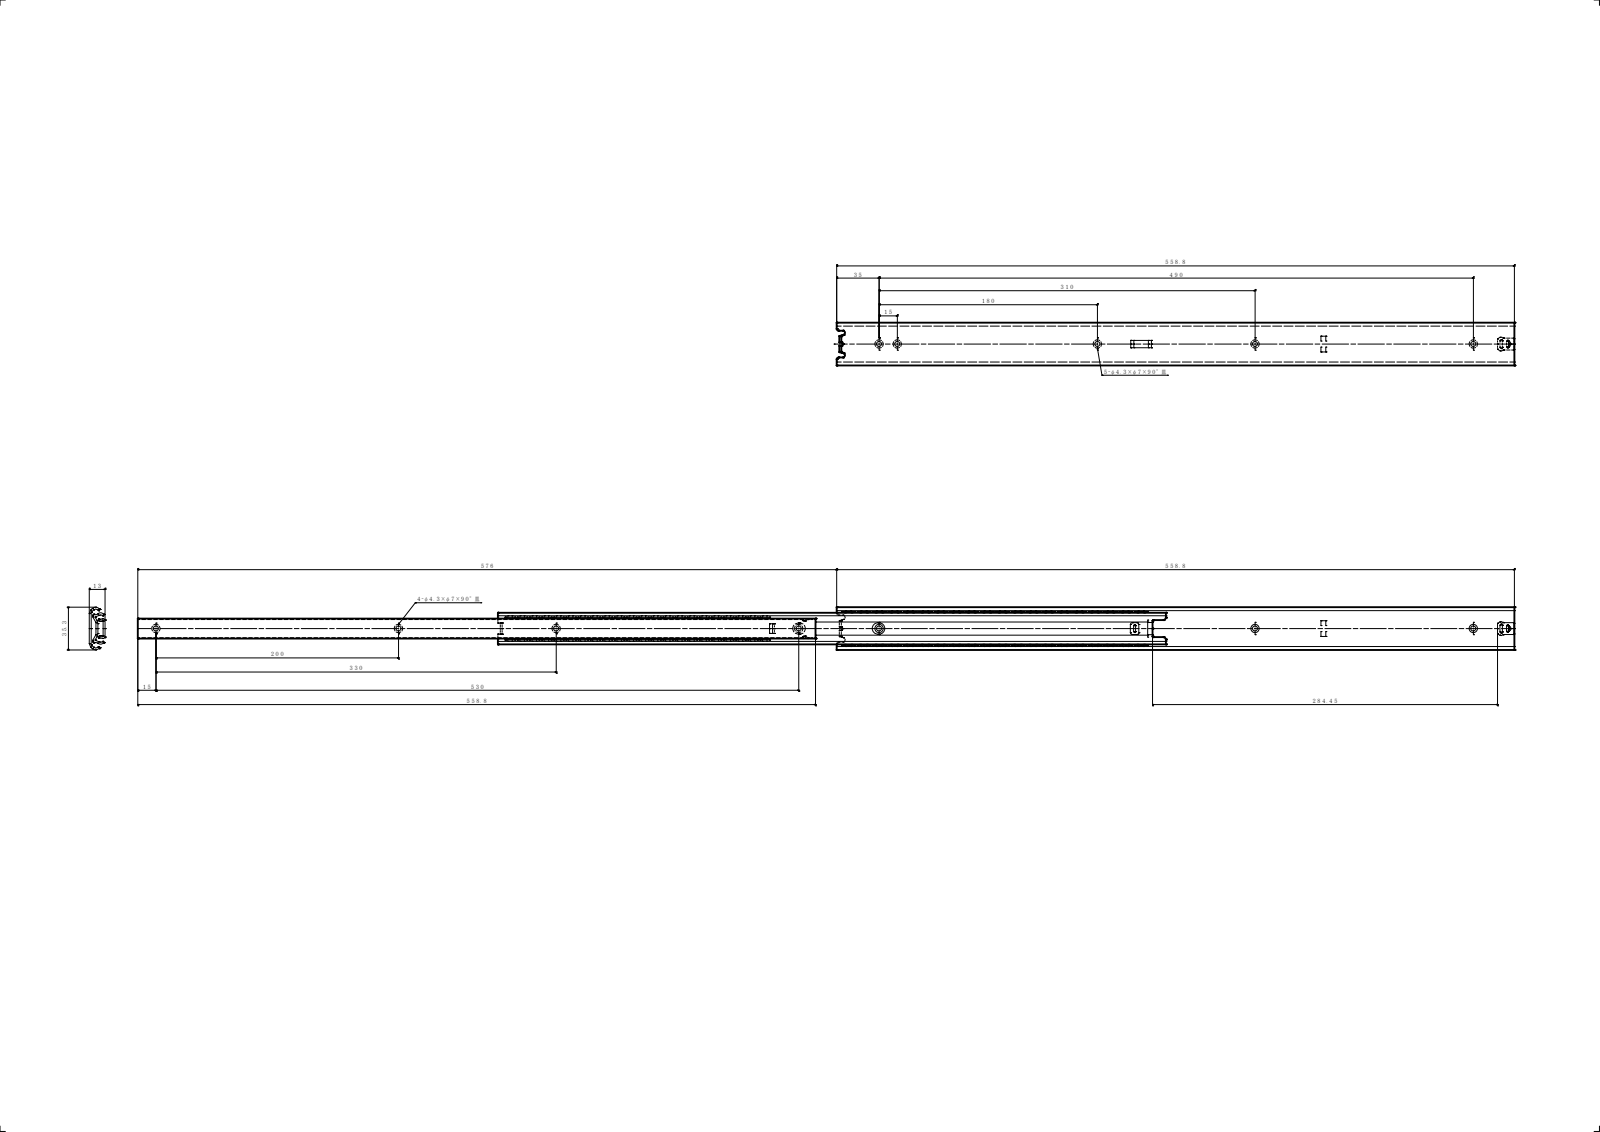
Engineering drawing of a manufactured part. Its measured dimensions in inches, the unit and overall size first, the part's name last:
Units: inches
Overall size (bounding box): 44.689 × 1.39 × 0.512
Round holes (diameter × count): ⌀0.169 ×9, ⌀0.177 ×1
Partial cylindrical surfaces — rounded edges, fillets, slot ends (radius × count): R0.02 ×21, R0.118 ×10, R0.059 ×8, R0.012 ×6, R0.079 ×6, R0.031 ×4, R0.039 ×4, R0.063 ×4
Main face-to-face distances: 0.063, 0.449, 0.213, 0.236, 0.512, 0.386, 0.15, 0.299, 0.276, 0.173
Hole centre spacings: 5.118, 7.087, 7.874, 12.205, 12.992, 22.689, 0.591, 1.267
Volume: 5.979 in³ · Surface area: 196.8 in²
Bodies: 5 solids, 300 faces (144 planar, 136 cylindrical, 20 other)
Part name (STEP PRODUCT): C351-22 IM; C351-22; C351-22 OM; PN32 (+2 more)
STEP written by: SolidWorks 2019 (CONFIG_CONTROL_DESIGN)
